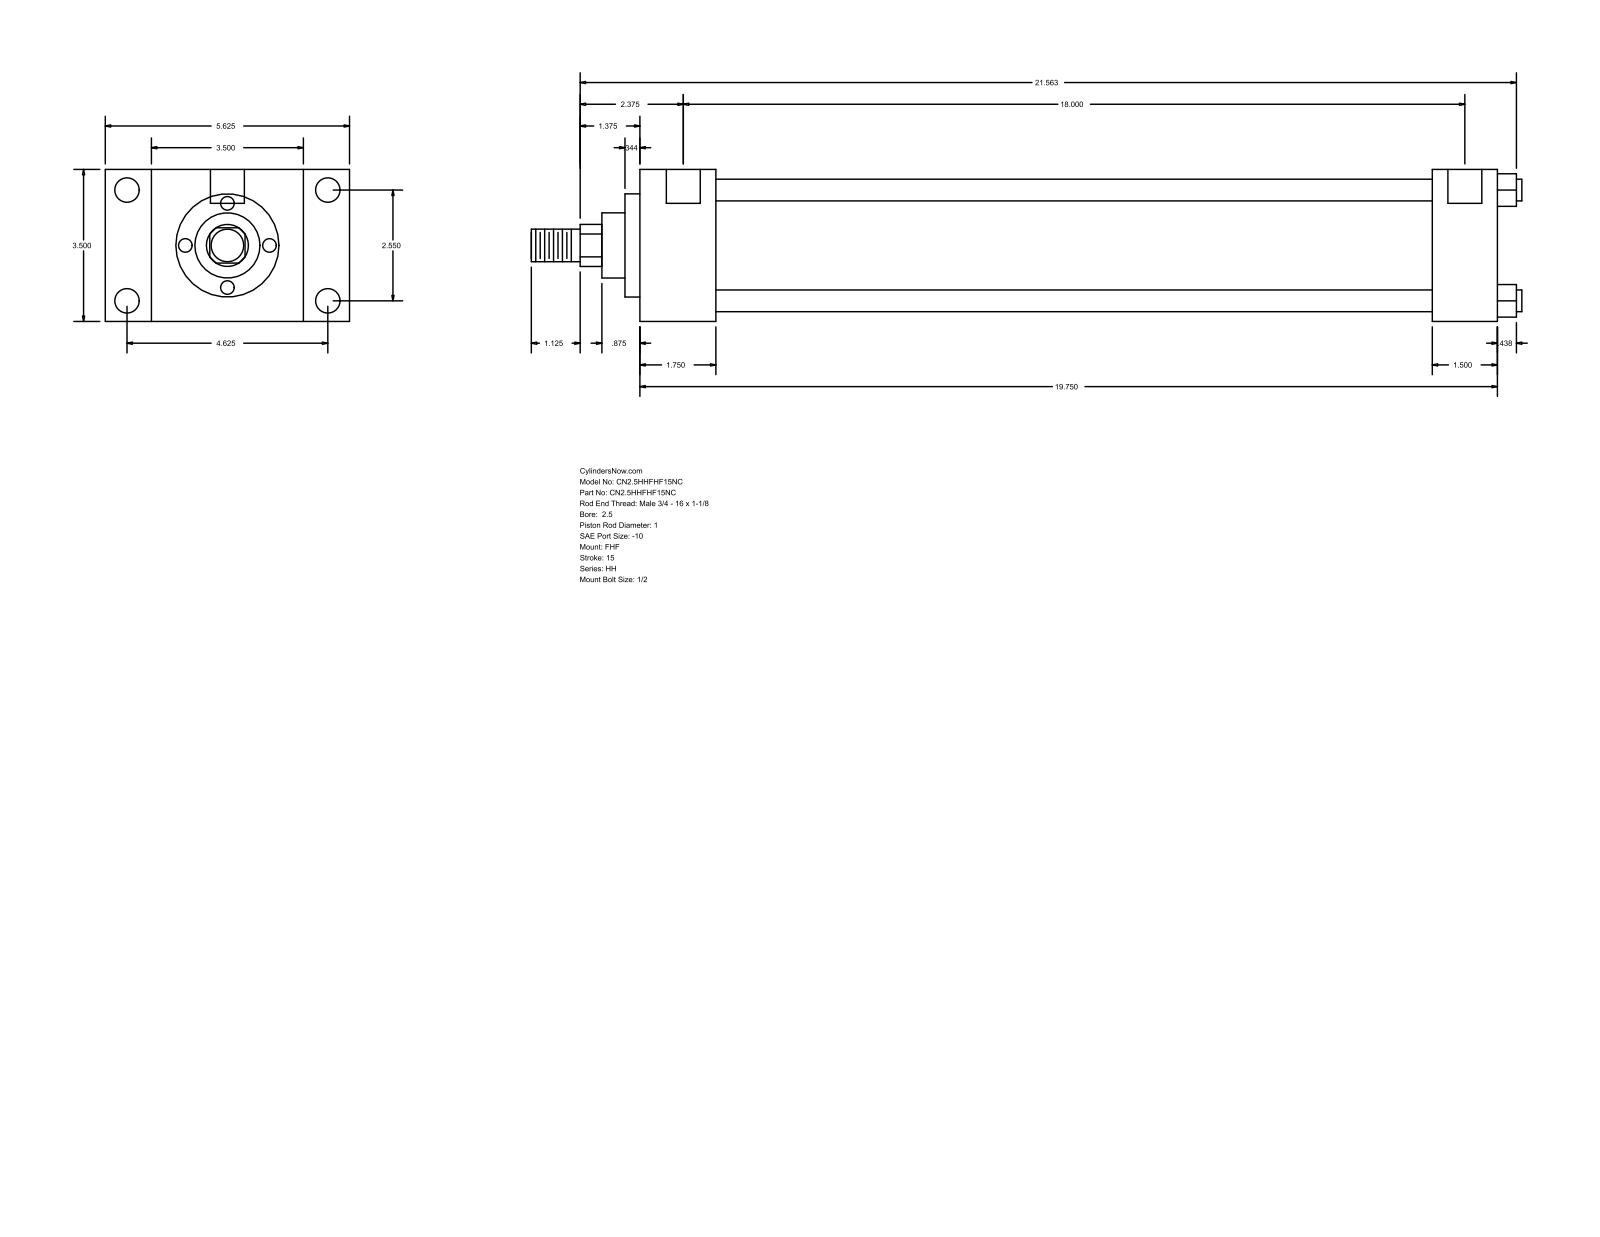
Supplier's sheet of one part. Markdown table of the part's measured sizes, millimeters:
| quantity | value |
| --- | --- |
| part name | HH_FHF__0250_1 |
| STEP written by | GSSL Pune (CONFIG_CONTROL_DESIGN) |
| units | millimeters |
| bodies | 0 solids, 90 faces (61 planar, 29 cylindrical, 0 other) |
| overall size | 579.44 × 142.88 × 88.9 |
| round holes (diameter × count) | 5.56 × 4, 14.3 × 4, 19.84 × 2 |
| round bosses / shafts (diameter × count) | 12.7 × 4, 73.03 × 1, 60.33 × 1, 38.1 × 1, 25.4 × 1, 19.05 × 1 |
| partial cylindrical surfaces (radius × count) | 12.29 × 1 |
| main face-to-face distances | 88.9, 44.46, 26.99, 115.89, 501.66, 457.2, 142.88, 38.1, 463.56, 419.1 |
| hole center spacings | 1.59, 64.76, 117.48, 134.15, 458.78, 460.37, 457.19 |
